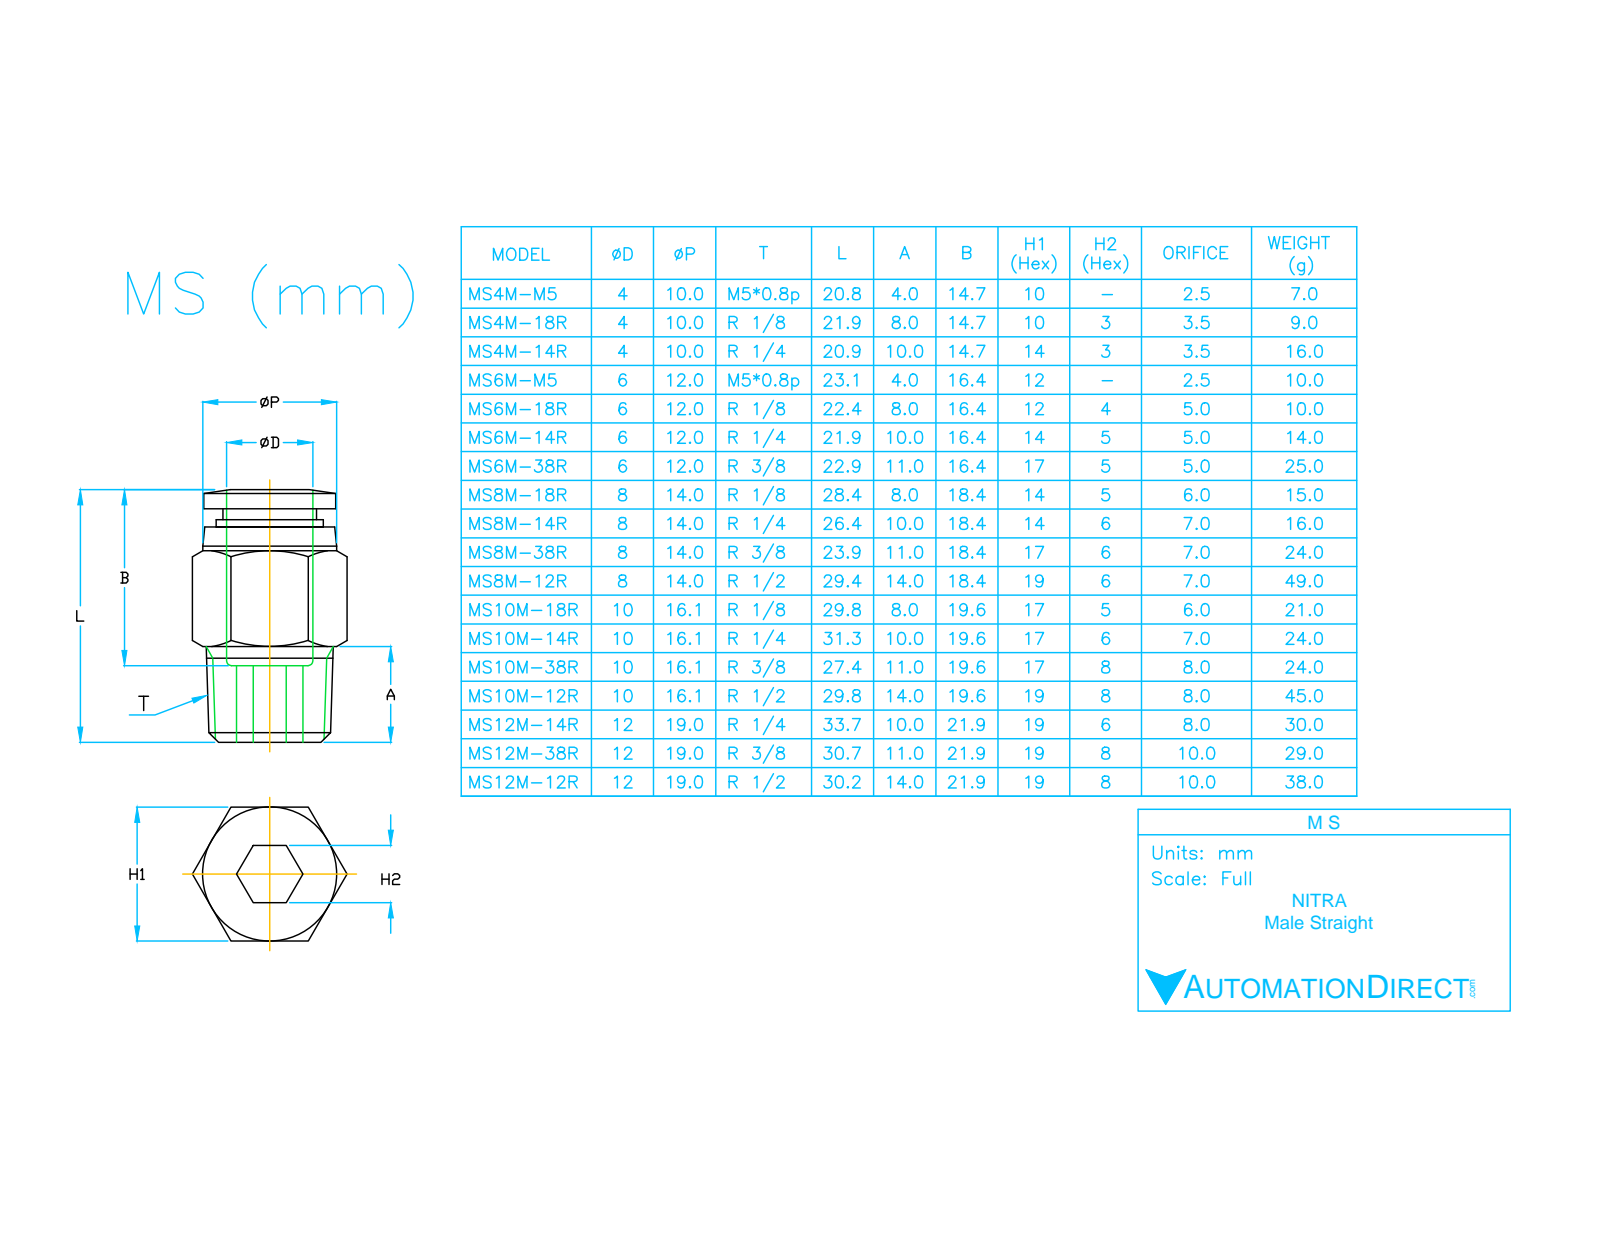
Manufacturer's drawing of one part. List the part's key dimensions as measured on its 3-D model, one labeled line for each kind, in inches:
Part name (STEP PRODUCT): MS4M-M5
STEP written by: SolidWorks 2018 (AUTOMOTIVE_DESIGN)
Units: inches
Bodies: 2 solids, 71 faces (17 planar, 22 cylindrical, 32 other)
Overall size (bounding box): 0.821 × 0.455 × 0.394
Volume: 0.066 in³ · Surface area: 1.786 in²
Round holes (diameter × count): ⌀0.098 ×1, ⌀0.169 ×1
Round bosses / shafts (diameter × count): ⌀0.394 ×1, ⌀0.382 ×1, ⌀0.374 ×1, ⌀0.299 ×1, ⌀0.283 ×1, ⌀0.22 ×1, ⌀0.197 ×1, ⌀0.157 ×1
Main face-to-face distances: 0.394, 0.049, 0.508, 0.557, 0.516, 0.565, 0.522, 0.514, 0.043, 0.053
